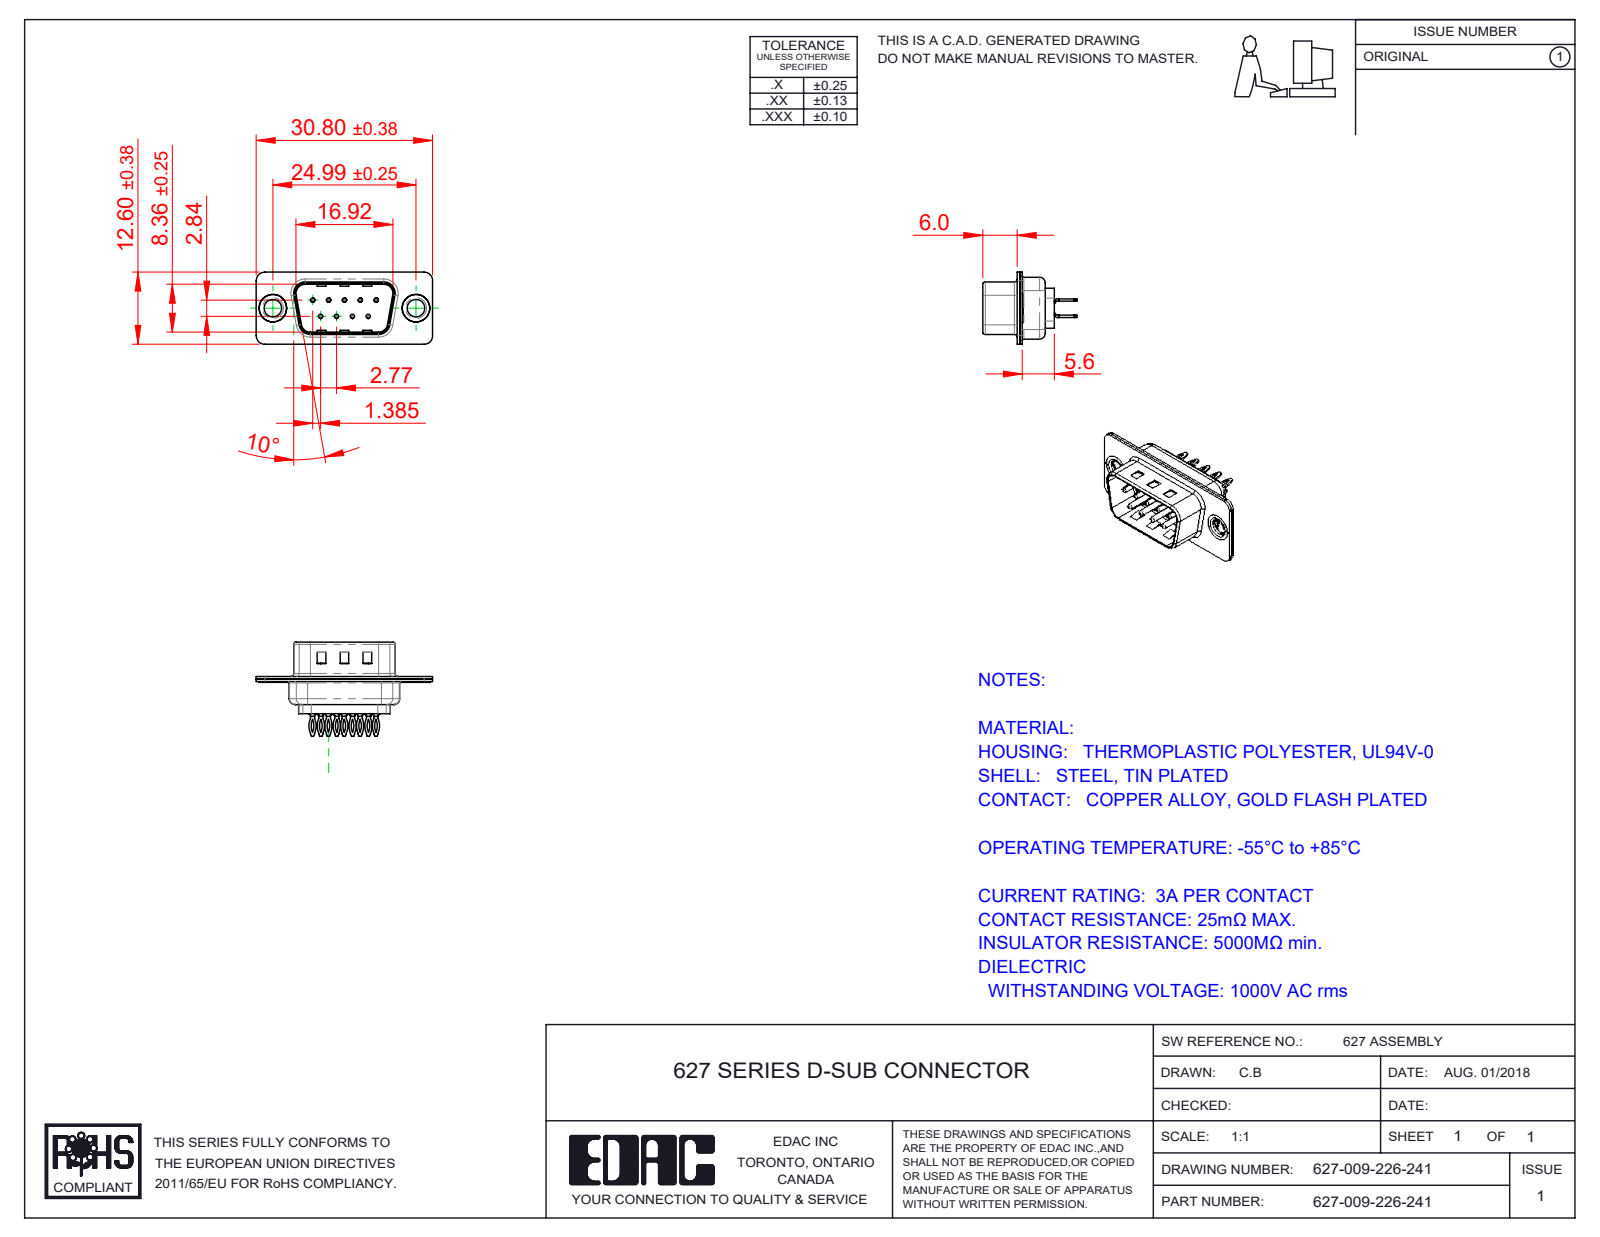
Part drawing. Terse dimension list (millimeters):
name: 627-009-226-041; 627 Contact Row 1_26L; 627 Housing_09 LP; 627 Shell Rear_09 Contacts (+3 more)
written by: SolidWorks 2020 (CONFIG_CONTROL_DESIGN)
unit: mm
bodies: 14 solids, 962 faces (287 planar, 392 cylindrical, 283 other)
size: 30.8 × 16.45 × 12.6
volume: 1 234 mm³; area: 3 761 mm²
holes: 9× ⌀0.35, 9× ⌀1.1, 9× ⌀1.6, 2× ⌀3.05, 2× ⌀4, 2× ⌀4.8
bosses: 9× ⌀2, 9× ⌀1.5, 9× ⌀0.75, 2× ⌀5, 2× ⌀4.9, 2× ⌀3.55
rounds: 18× R1.5, 18× R2.92, 18× R3.33, 12× R2, 8× R0.5, 8× R1.6, 4× R0.25, 4× R0.6
face distances: 0.4, 0.45, 0.9, 0.82, 9.58, 1.4, 0.5, 8.76, 1.5, 6.05
hole spacings: 3.16, 2.77, 5.54, 5.03, 5.04, 8.31, 7.48, 7.49
